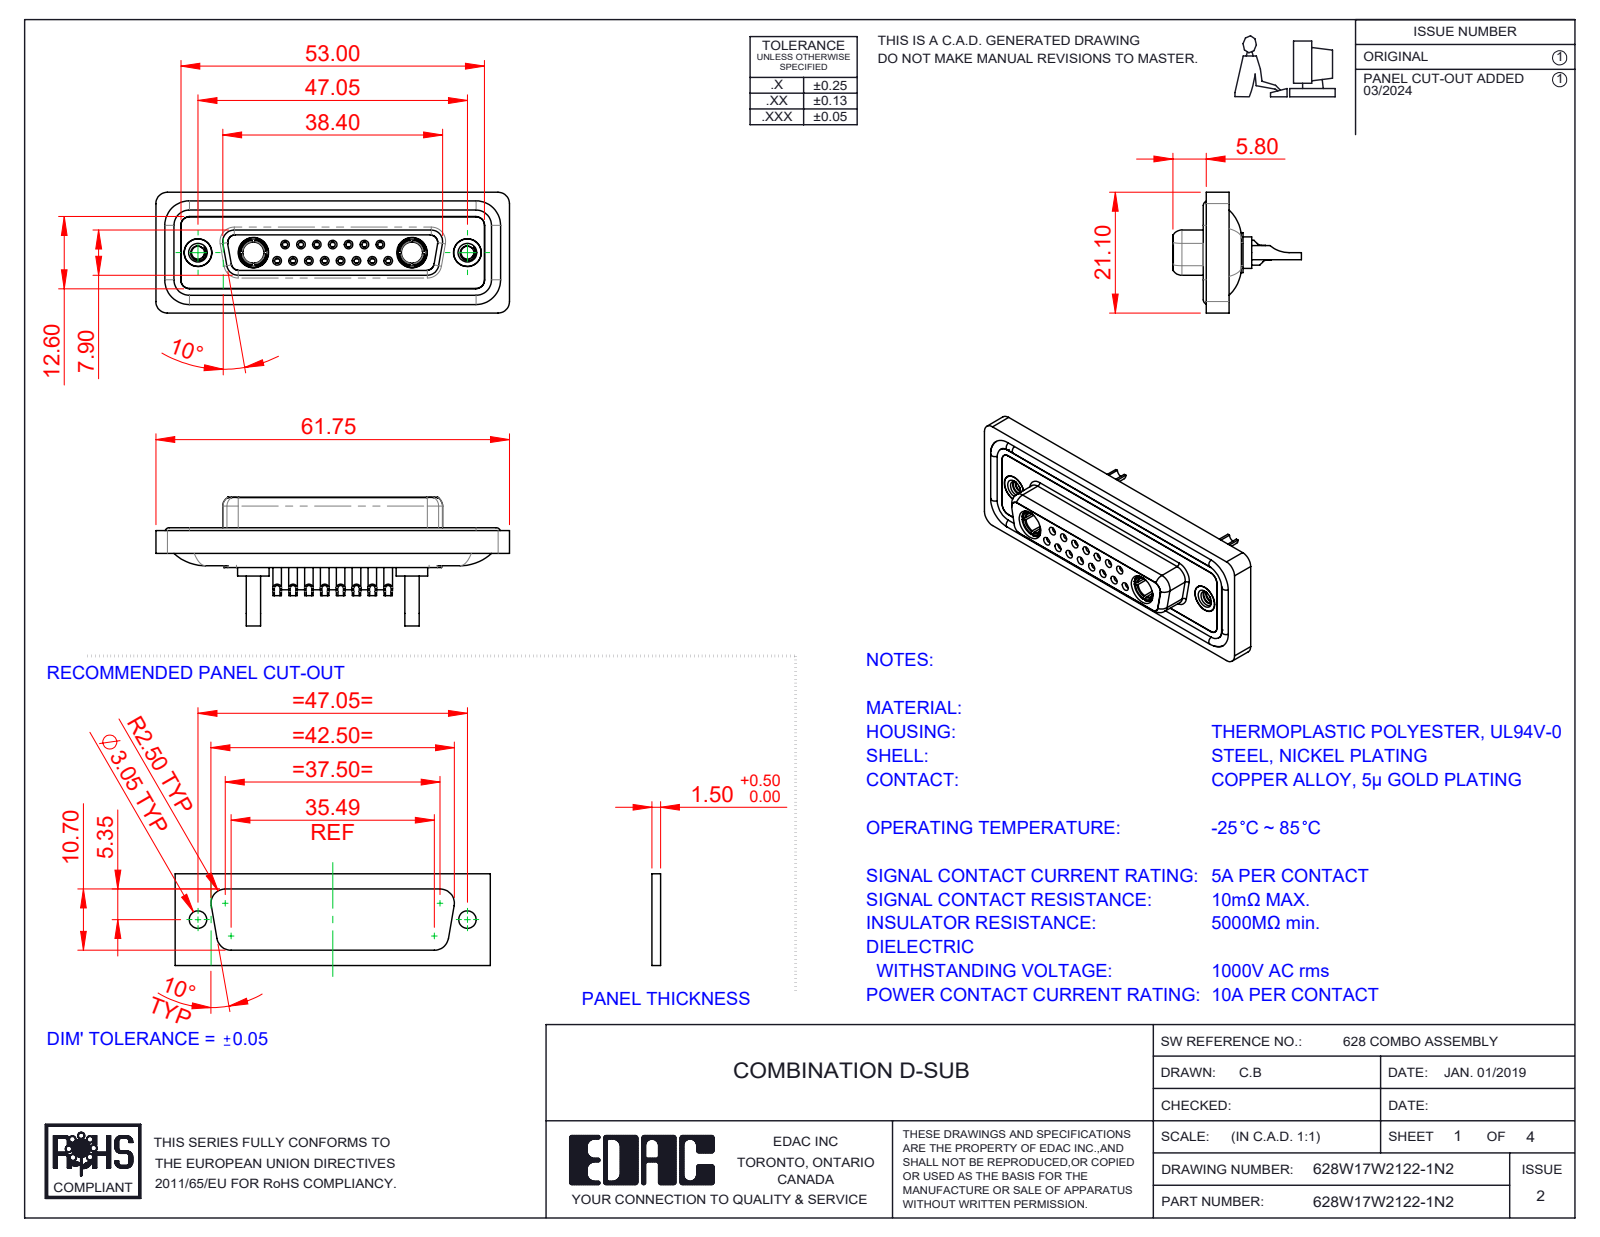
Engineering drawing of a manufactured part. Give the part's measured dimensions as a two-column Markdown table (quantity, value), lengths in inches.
| quantity | value |
| --- | --- |
| part name | 628Combo Waterproof Housing_25 Contacts; 628Combo Contact Row 2_22; 628Combo Threaded Rivet_2; 628Combo Shell Front_25 Contacts (+5 more) |
| STEP written by | SolidWorks 2023 (CONFIG_CONTROL_DESIGN) |
| units | inches |
| bodies | 26 solids, 1369 faces (422 planar, 555 cylindrical, 392 other) |
| overall size | 2.431 × 0.884 × 0.831 |
| volume | 0.51 in³ |
| surface area | 21.87 in² |
| round holes (diameter × count) | 0.035 × 15, 0.039 × 15, 0.043 × 15, 0.059 × 15, 0.079 × 15, 0.063 × 8, 0.067 × 7, 0.191 × 4, 0.067 × 2, 0.089 × 2, 0.146 × 2, 0.157 × 2 |
| round bosses / shafts (diameter × count) | 0.087 × 15, 0.063 × 11, 0.217 × 2, 0.205 × 2, 0.195 × 2, 0.195 × 2, 0.189 × 2, 0.187 × 2 |
| partial cylindrical surfaces (radius × count) | 0.059 × 22, 0.079 × 18, 0.053 × 8, 0.063 × 8, 0.039 × 6, 0.01 × 4, 0.02 × 4, 0.024 × 4 |
| main face-to-face distances | 0.016, 0.071, 0.293, 0.222, 0.26, 0.02, 0.278, 0.063, 0.114, 0.043 |
| hole center spacings | 0.124, 0.109, 0.327, 0.218, 0.198, 0.198, 0.295, 0.436 |
